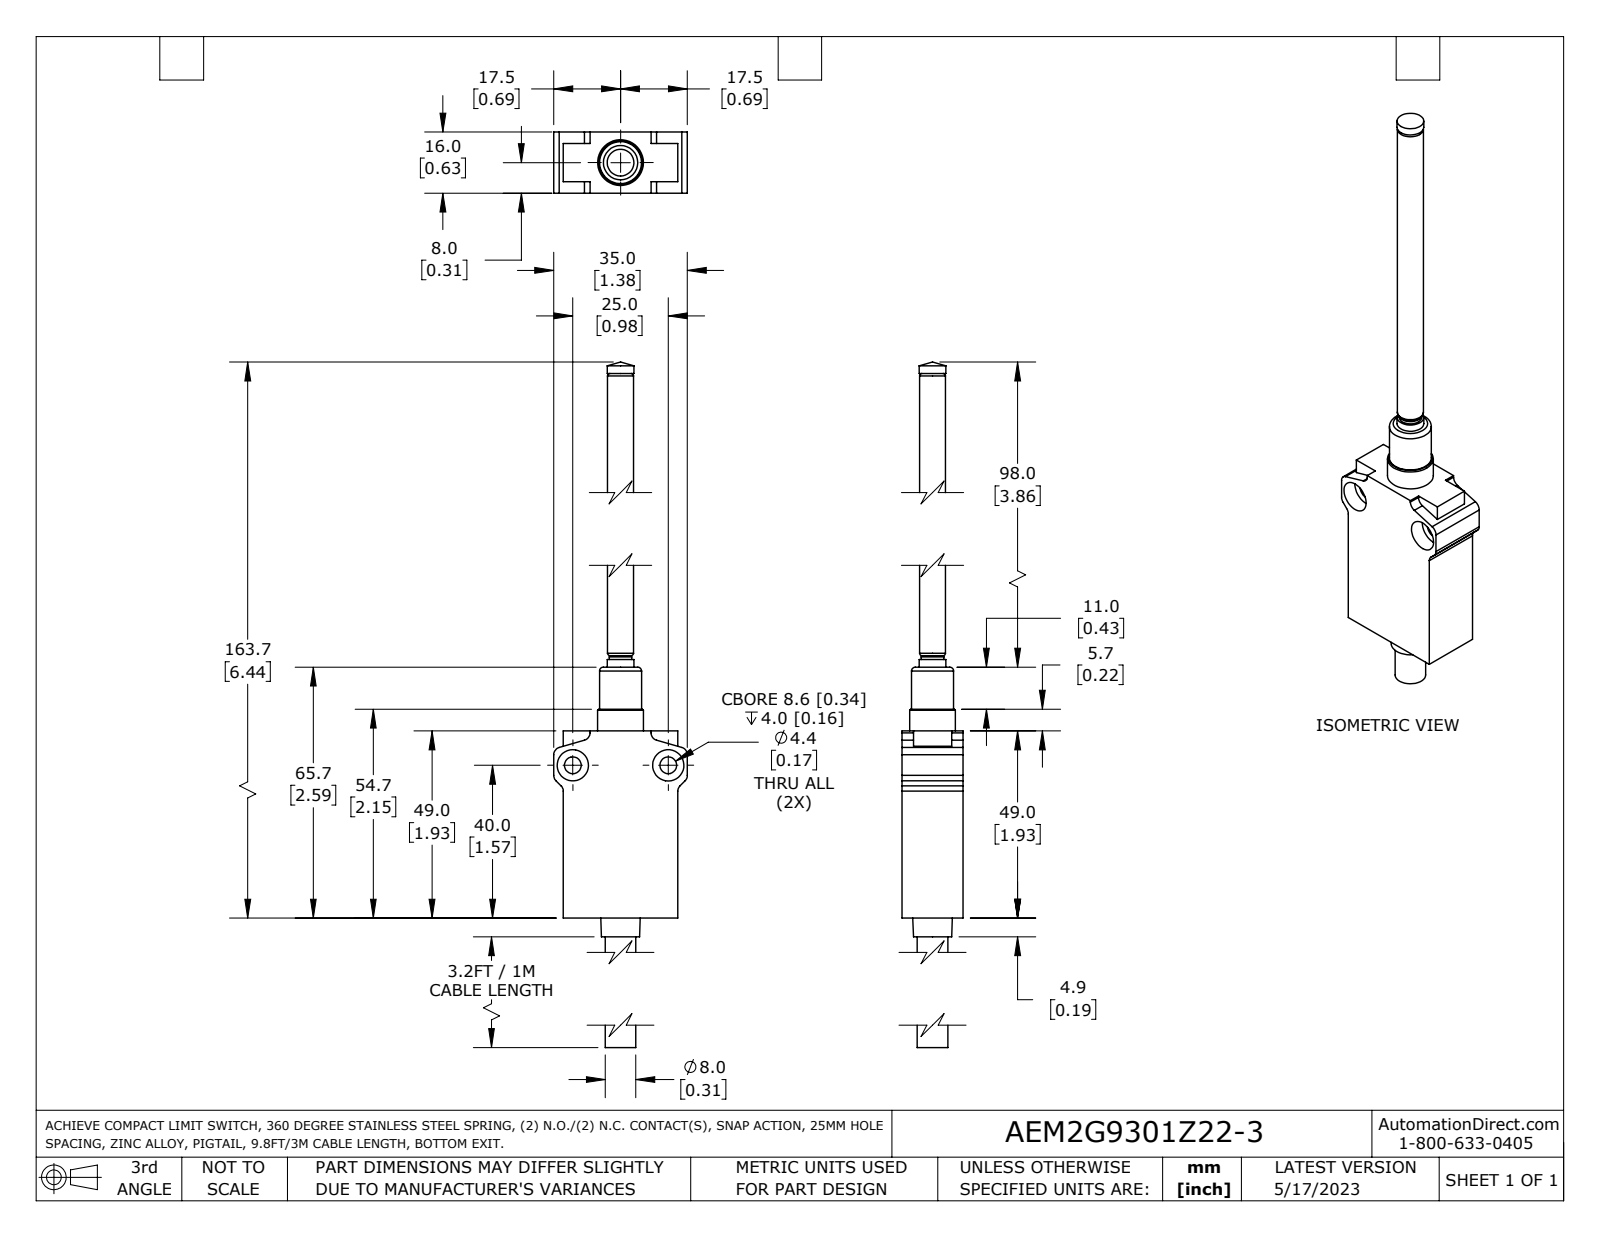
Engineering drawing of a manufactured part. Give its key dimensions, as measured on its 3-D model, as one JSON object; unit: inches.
{"part_name": "AEM2G9301Z22-3", "step_written_by": "SolidWorks 2021 (AUTOMOTIVE_DESIGN)", "units": "inches", "bodies": {"solids": 1, "faces": 83, "planar": 45, "cylindrical": 27, "other": 11}, "overall_size": [7.031, 1.378, 0.63], "volume_in3": 1.772, "surface_area_in2": 14.41, "round_holes": [[0.173, 2], [0.323, 2]], "round_bosses_or_shafts": [[0.472, 1], [0.433, 1], [0.315, 1], [0.276, 1], [0.268, 1], [0.232, 1]], "partial_cylinders_radius": [[0.079, 8], [0.256, 1]], "face_to_face_distances": [0.63, 1.181, 1.929, 0.098, 1.28, 0.472, 0.157, 0.512, 1.378, 0.039], "hole_center_spacings": [0.984]}
